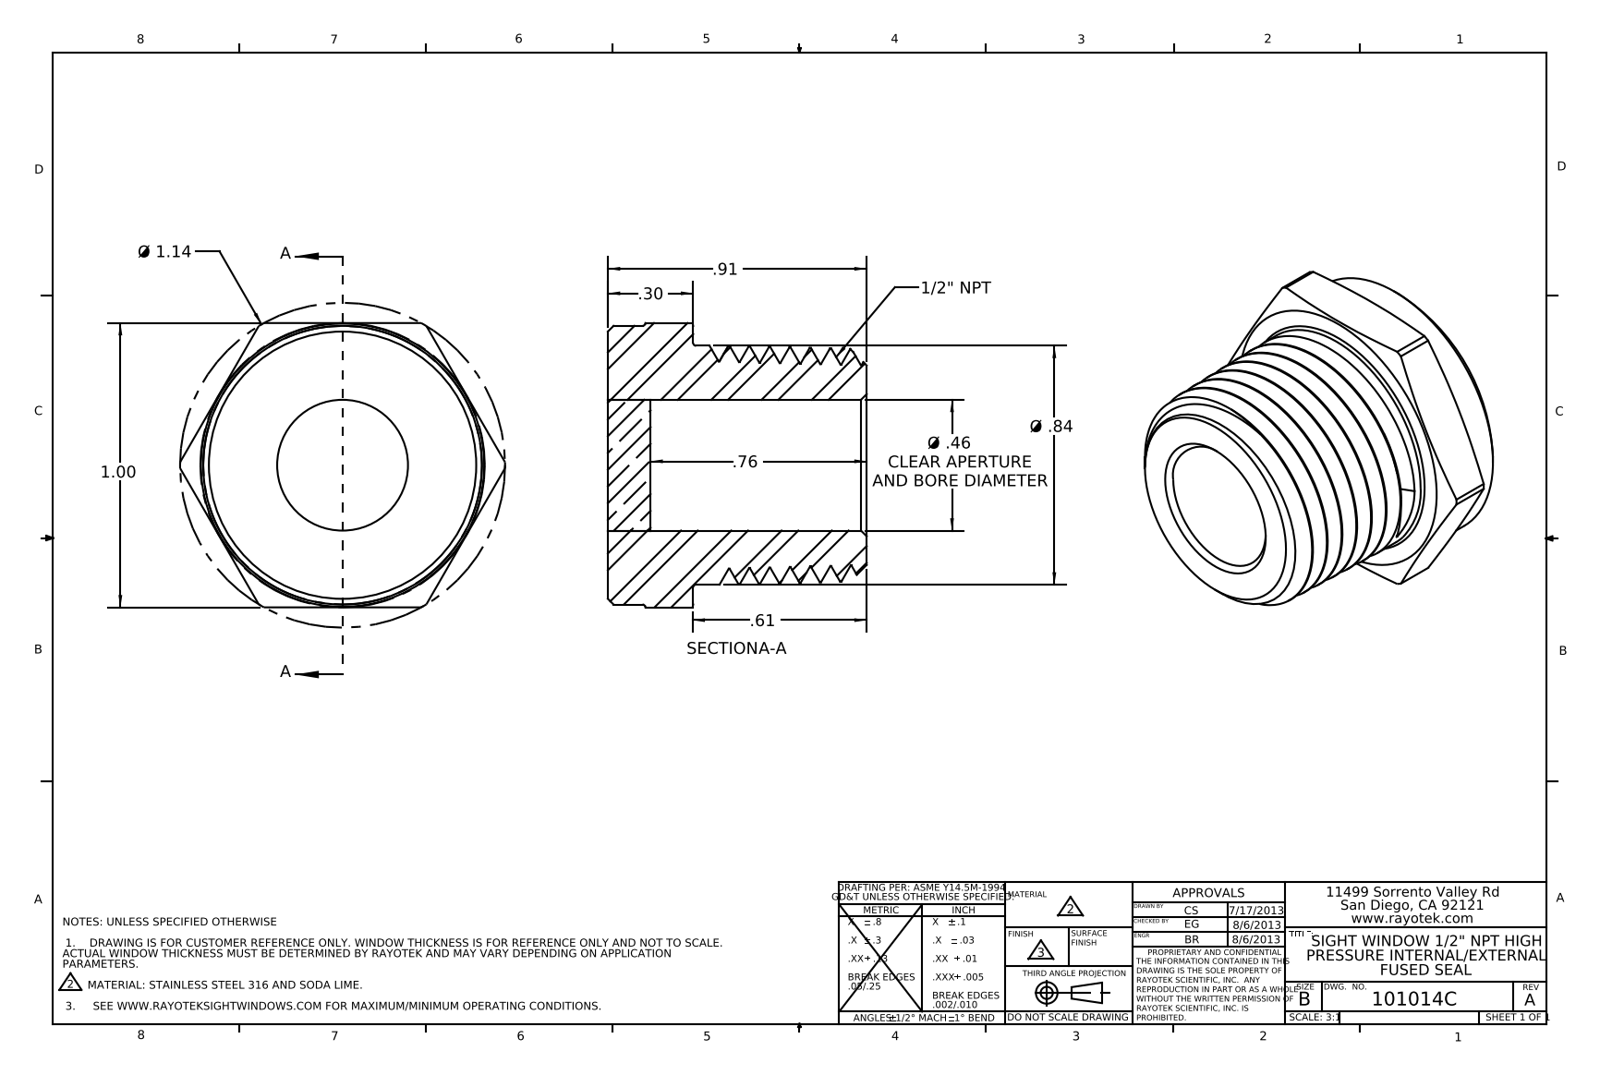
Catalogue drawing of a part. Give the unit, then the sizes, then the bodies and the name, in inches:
Units: inches
Overall size (bounding box): 1.143 × 1 × 0.91
Round holes (diameter × count): ⌀0.46 ×1
Round bosses / shafts (diameter × count): ⌀0.98 ×1, ⌀0.84 ×1
Partial cylindrical surfaces — rounded edges, fillets, slot ends (radius × count): R0.571 ×1
Main face-to-face distances: 0.15, 1, 0.91, 0.3, 0.61, 0.76
Volume: 0.409 in³ · Surface area: 6.603 in²
Bodies: 2 solids, 61 faces (14 planar, 16 cylindrical, 31 other)
Part name (STEP PRODUCT): 101014; 402014; 403014_CUSTOMER
STEP written by: SolidWorks 2012 (AUTOMOTIVE_DESIGN)
